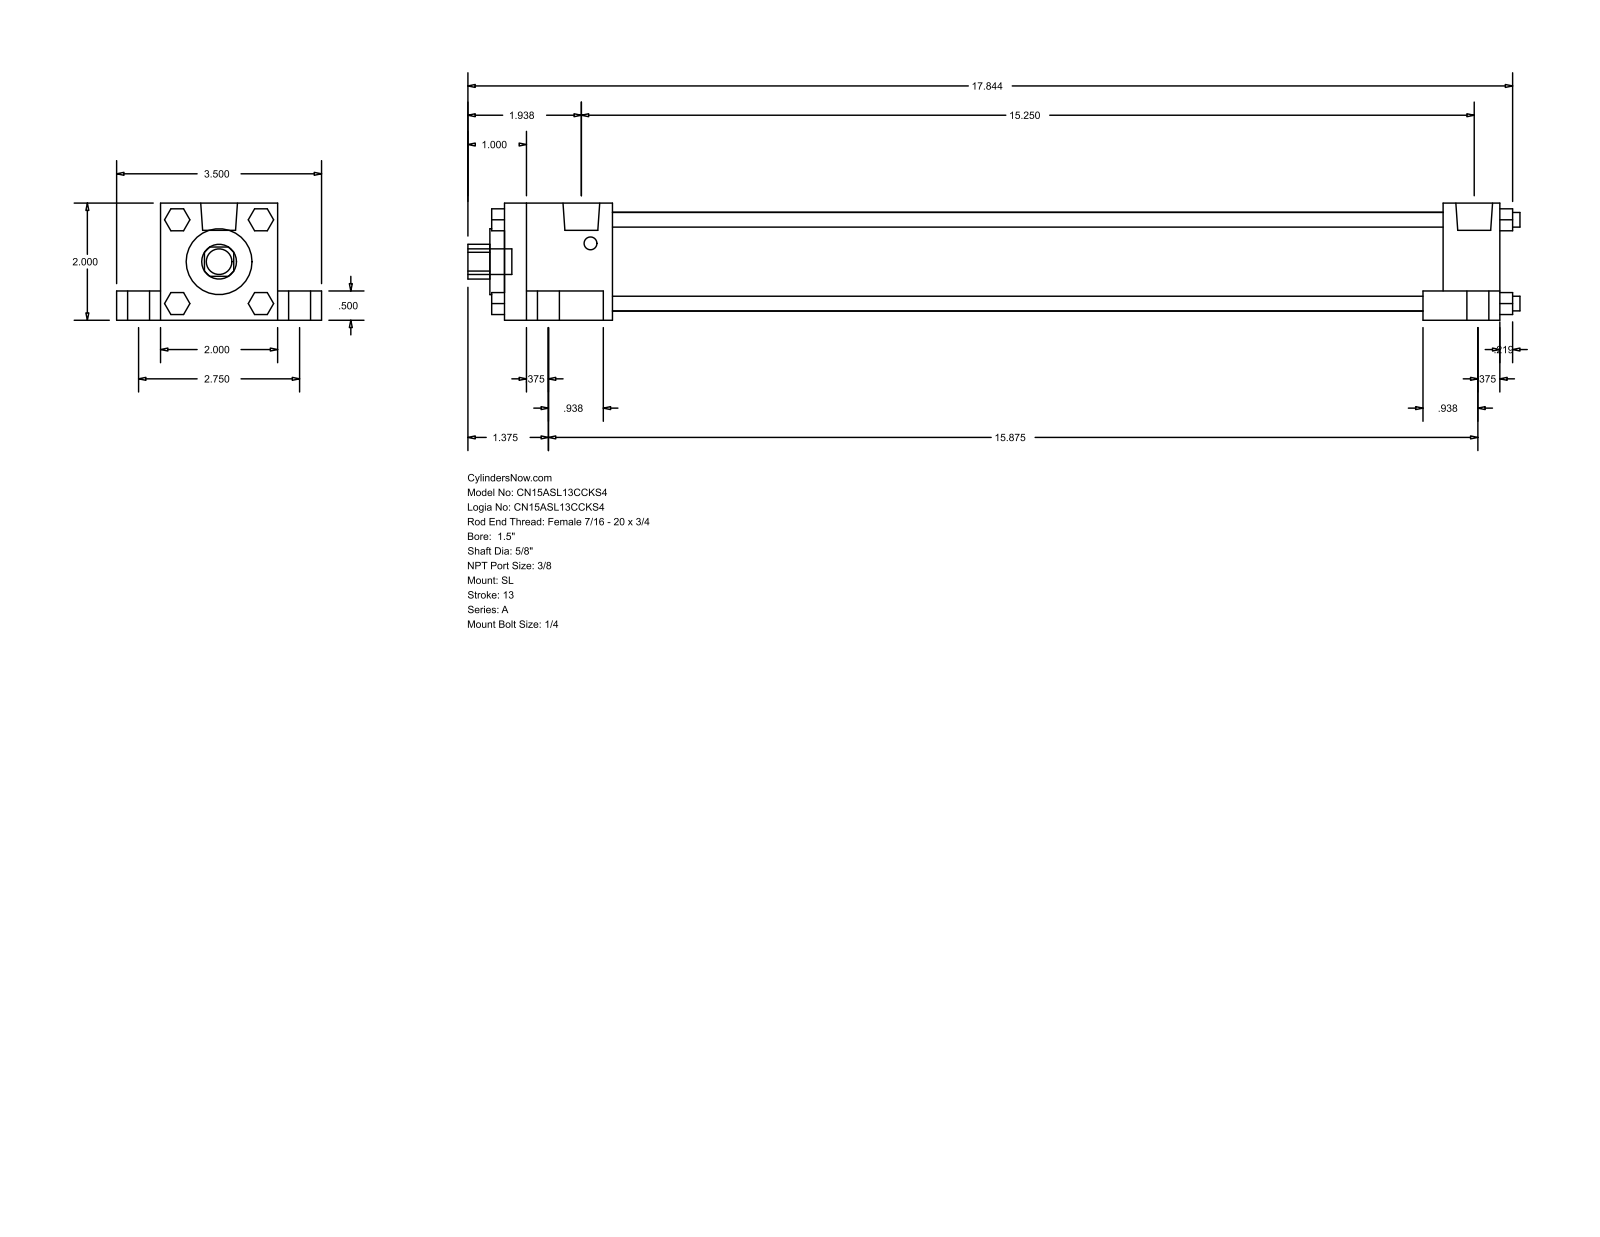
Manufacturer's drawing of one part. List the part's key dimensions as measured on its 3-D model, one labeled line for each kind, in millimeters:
Part name (STEP PRODUCT): A_SL__0150_0.625
STEP written by: GSSL Pune (CONFIG_CONTROL_DESIGN)
Units: millimetres
Bodies: 0 solids, 148 faces (112 planar, 36 cylindrical, 0 other)
Overall size (bounding box): 456.41 × 88.9 × 50.8
Round holes (diameter × count): ⌀15.88 ×1, ⌀28.57 ×1, ⌀42.93 ×1
Round bosses / shafts (diameter × count): ⌀15.88 ×4, ⌀9.53 ×4, ⌀6.35 ×4, ⌀5.56 ×4, ⌀15.93 ×2, ⌀11.11 ×1
Partial cylindrical surfaces — rounded edges, fillets, slot ends (radius × count): R7.54 ×1
Main face-to-face distances: 50.8, 19.05, 12.7, 38.1, 69.85, 431.8, 9.52, 33.34, 407.19, 24.61
